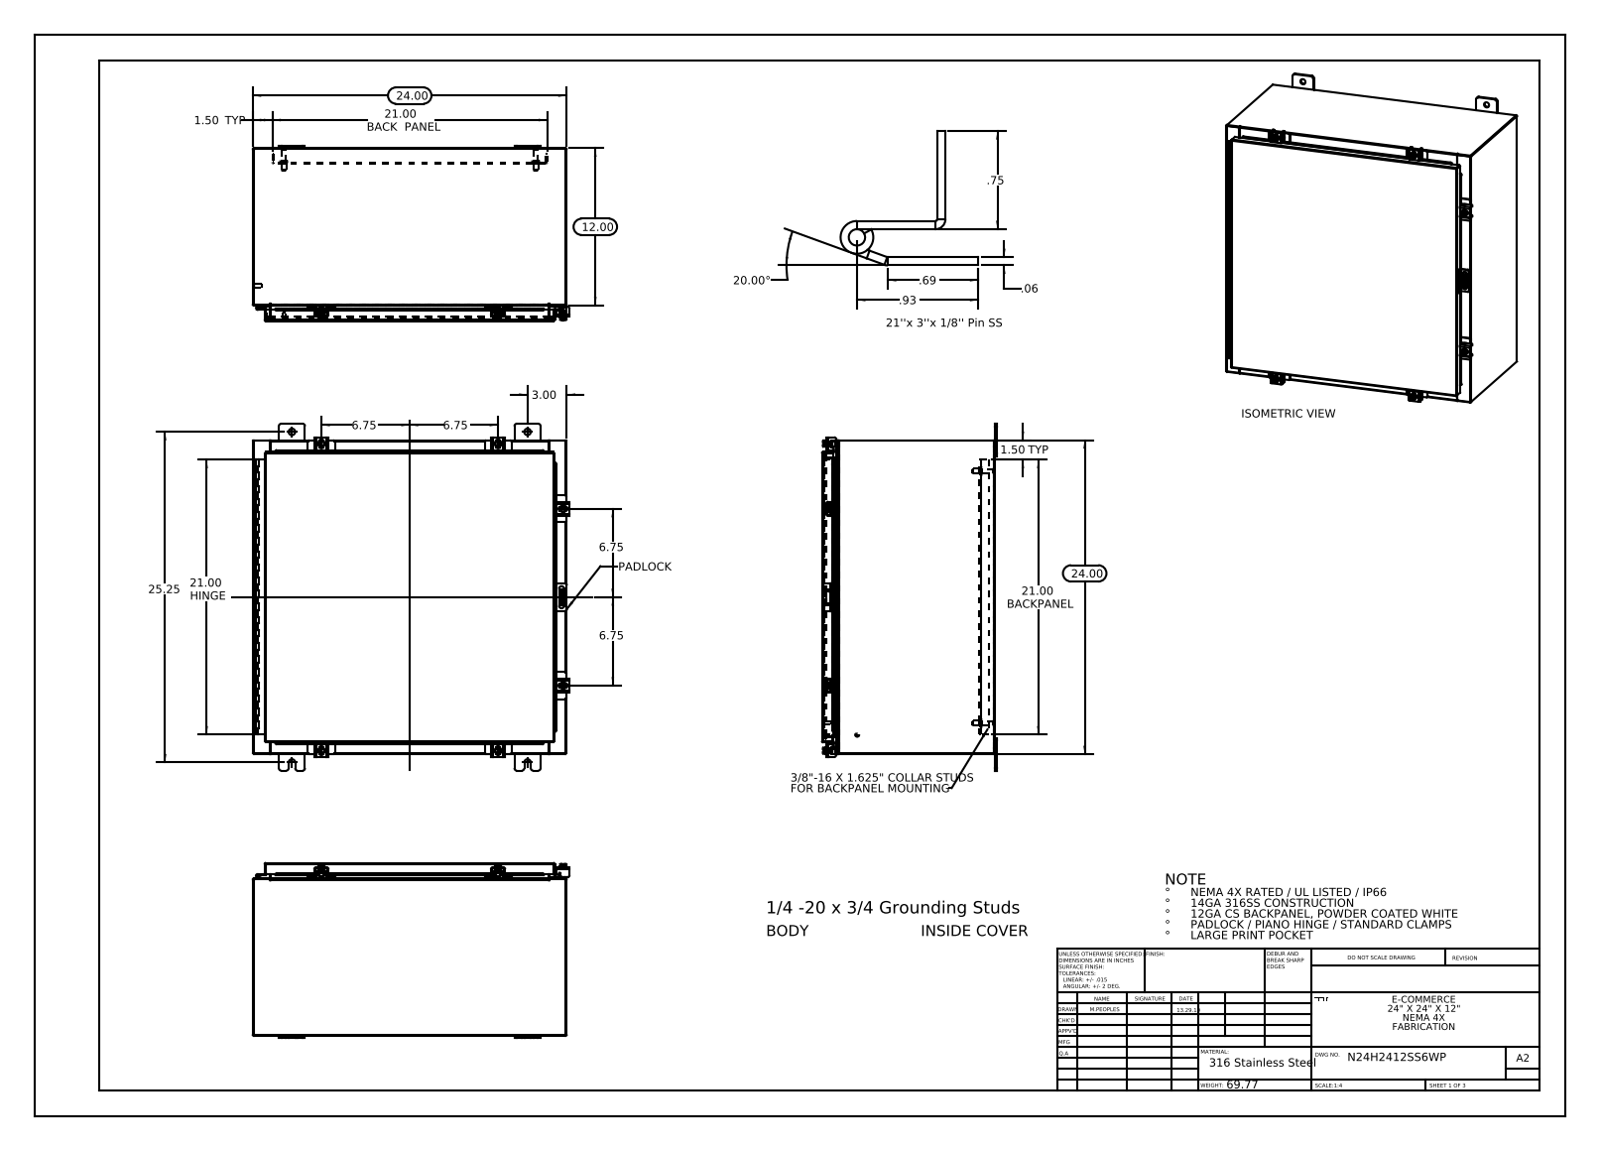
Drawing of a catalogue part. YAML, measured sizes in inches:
part_name: "N24H2412SS6WP Mounting Studs; N24H2412SS6WP Cover; N24H2412SS6WP 125 Pin Hinge; N24H2412SS6WP Padlock Staple (+8 more)"
step_written_by: "SolidWorks 2013 (CONFIG_CONTROL_DESIGN)"
units: inches
bodies: {solids: 47, faces: 1709, planar: 908, cylindrical: 705, other: 96}
overall_size: [26.5, 24.211, 13.389]
volume: 244.7
surface_area: 6196
round_holes:
  - {diameter: 0.5, count: 8}
  - {diameter: 0.213, count: 6}
  - {diameter: 0.26, count: 6}
  - {diameter: 0.125, count: 2}
  - {diameter: 0.125, count: 1}
round_bosses_or_shafts:
  - {diameter: 0.25, count: 7}
  - {diameter: 0.5, count: 6}
  - {diameter: 0.399, count: 6}
  - {diameter: 0.625, count: 4}
  - {diameter: 0.375, count: 4}
  - {diameter: 0.33, count: 4}
partial_cylinders:
  - {radius: 0.06, count: 30}
  - {radius: 0.013, count: 25}
  - {radius: 0.19, count: 24}
  - {radius: 0.088, count: 21}
  - {radius: 0.12, count: 12}
  - {radius: 0.141, count: 12}
  - {radius: 0.125, count: 10}
  - {radius: 0.05, count: 9}
face_to_face_distances: [0.075, 23.925, 13.126, 23.85, 24, 13.201, 13.051, 0.104, 1, 1.075]
hole_center_spacings: [16.509, 19.134, 21.544, 26.907, 13.5, 1.858, 2.277, 2.423]
